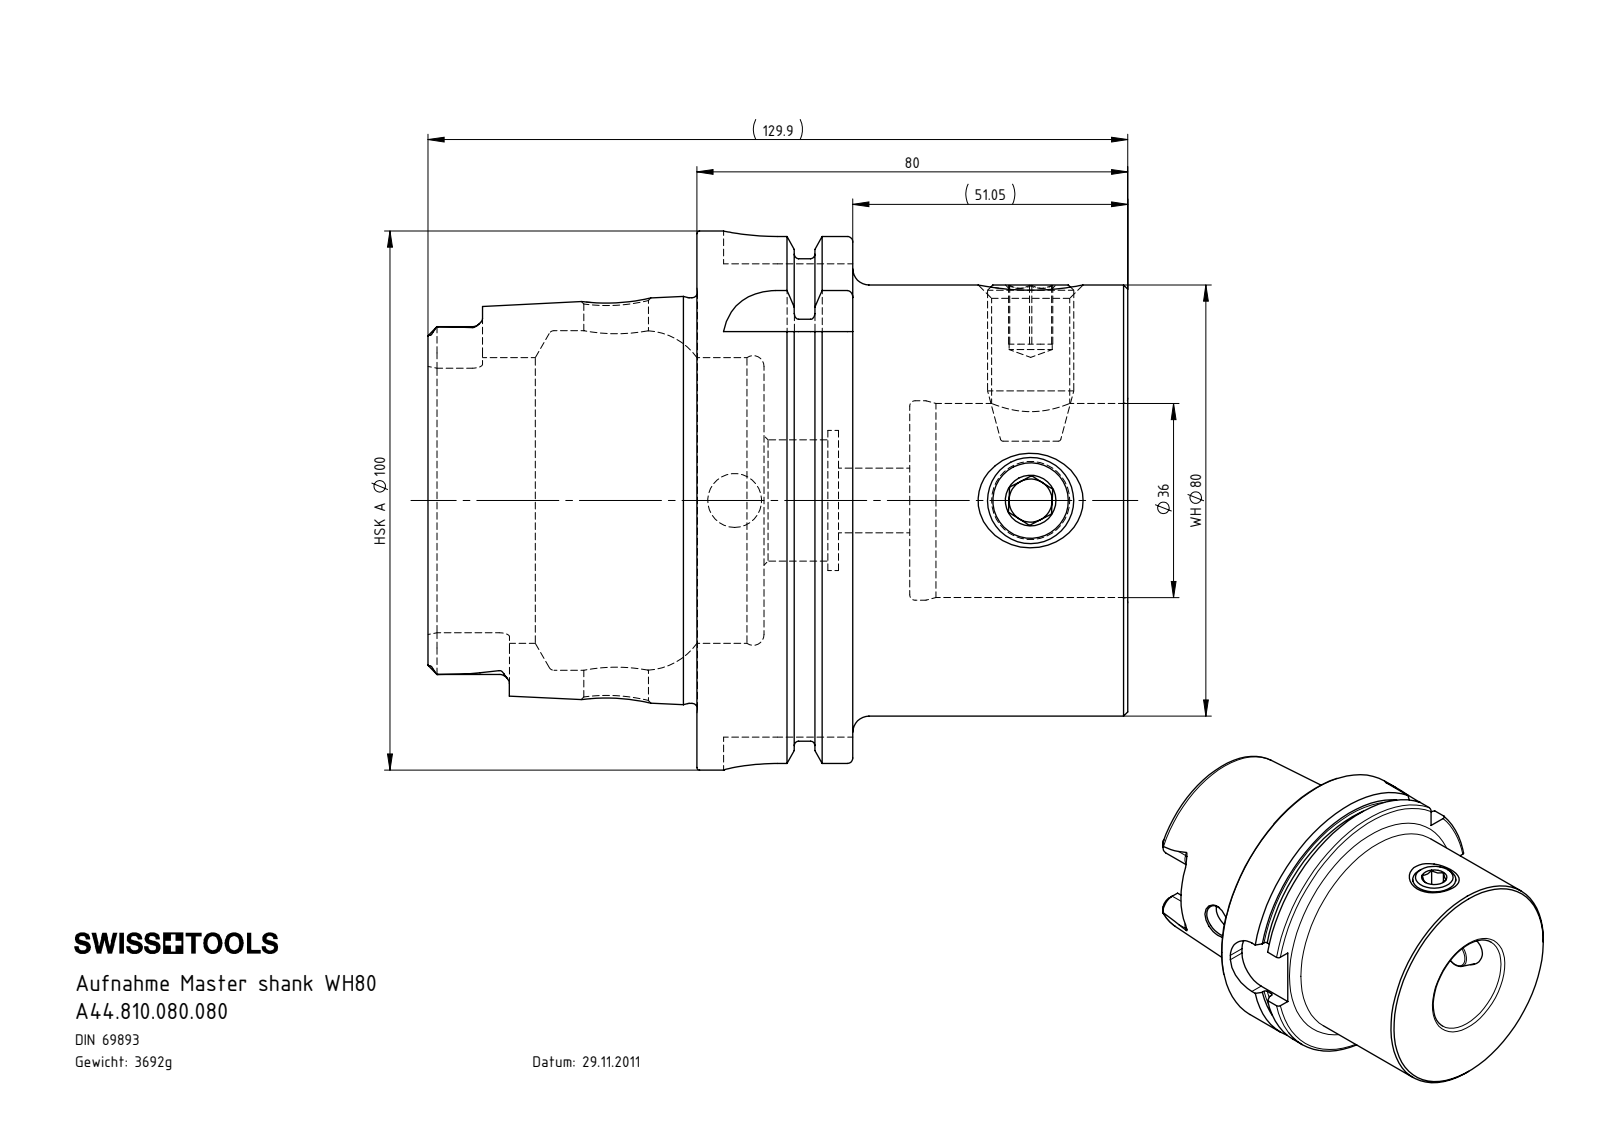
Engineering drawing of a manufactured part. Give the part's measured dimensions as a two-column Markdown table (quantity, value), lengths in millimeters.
| quantity | value |
| --- | --- |
| part name | WH8-ER1.001.029; HA0-WH8.K01.080_A_Fertigbearbeitung; A44.810.080.080 |
| STEP written by | SolidWorks 2015 (AUTOMOTIVE_DESIGN) |
| units | millimeters |
| bodies | 3 solids, 200 faces (59 planar, 58 cylindrical, 83 other) |
| overall size | 129.9 × 100 × 100 |
| volume | 469 667 mm³ |
| surface area | 72 167 mm² |
| round holes (diameter × count) | 12 × 2, 14.5 × 2, 10 × 1, 22.5 × 1, 26 × 1, 36 × 1, 37 × 1, 53 × 1, 63 × 1 |
| round bosses / shafts (diameter × count) | 16 × 2, 100 × 1, 91.95 × 1, 80 × 1, 75.26 × 1 |
| partial cylindrical surfaces (radius × count) | 1.9 × 6, 4.88 × 4, 10 × 4 |
| main face-to-face distances | 80, 28.95, 51.05, 12.45, 16.5, 67.55, 49.9, 62.35, 78.85, 129.9 |
| hole center spacings | 54.95, 76.95 |
